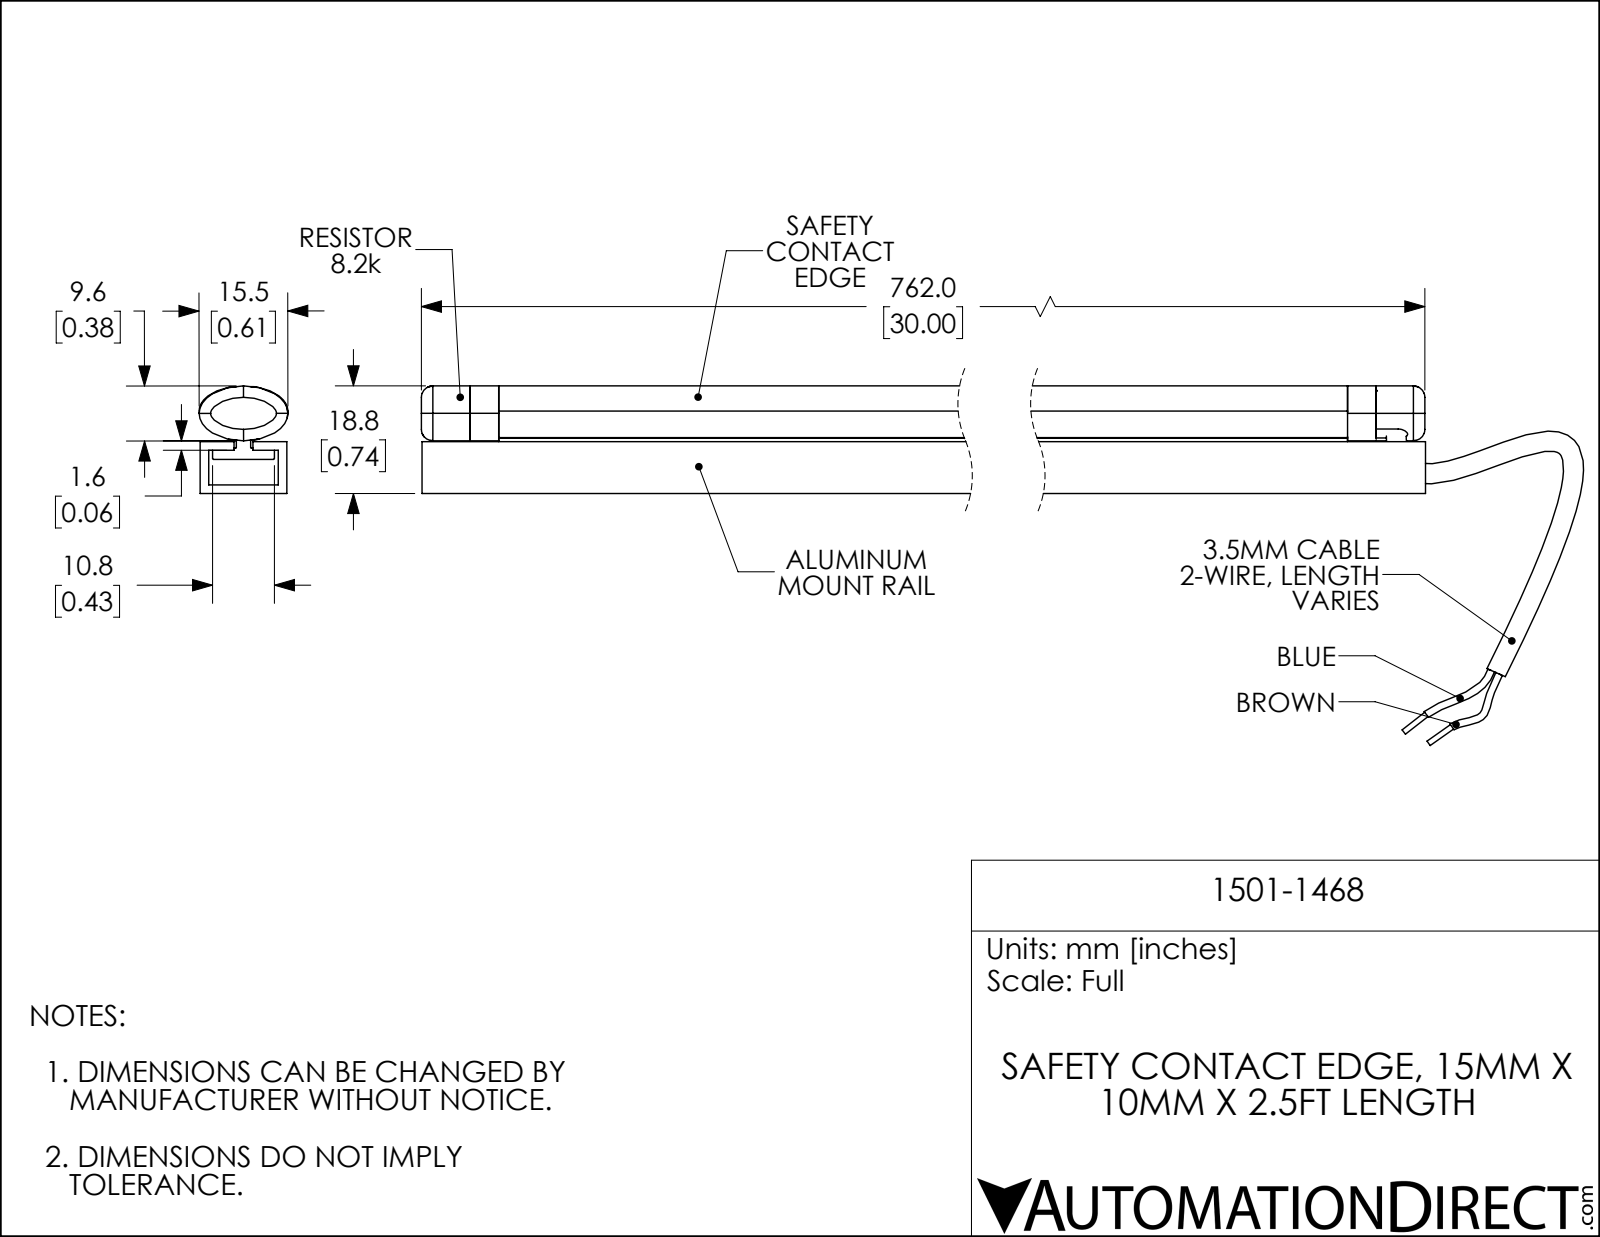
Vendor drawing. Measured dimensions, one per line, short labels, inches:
name: 1501-1468
written by: SolidWorks 2018 (AUTOMOTIVE_DESIGN)
unit: in
bodies: 7 solids, 607 faces (129 planar, 154 cylindrical, 324 other)
size: 31.091 × 2.472 × 0.611
volume: 7.435 in³; area: 211.9 in²
holes: 4× ⌀0.047
bosses: 2× ⌀0.037
rounds: 52× R0.004, 15× R0.016, 10× R0.012, 7× R0.008, 4× R0.02, 4× R0.512, 3× R0.008, 3× R0.059
face distances: 0.059, 0.297, 0.537, 0.356, 0.016, 0.122, 0.234, 0.175, 0.596, 0.238
hole spacings: 0.197, 0.196, 0.197
